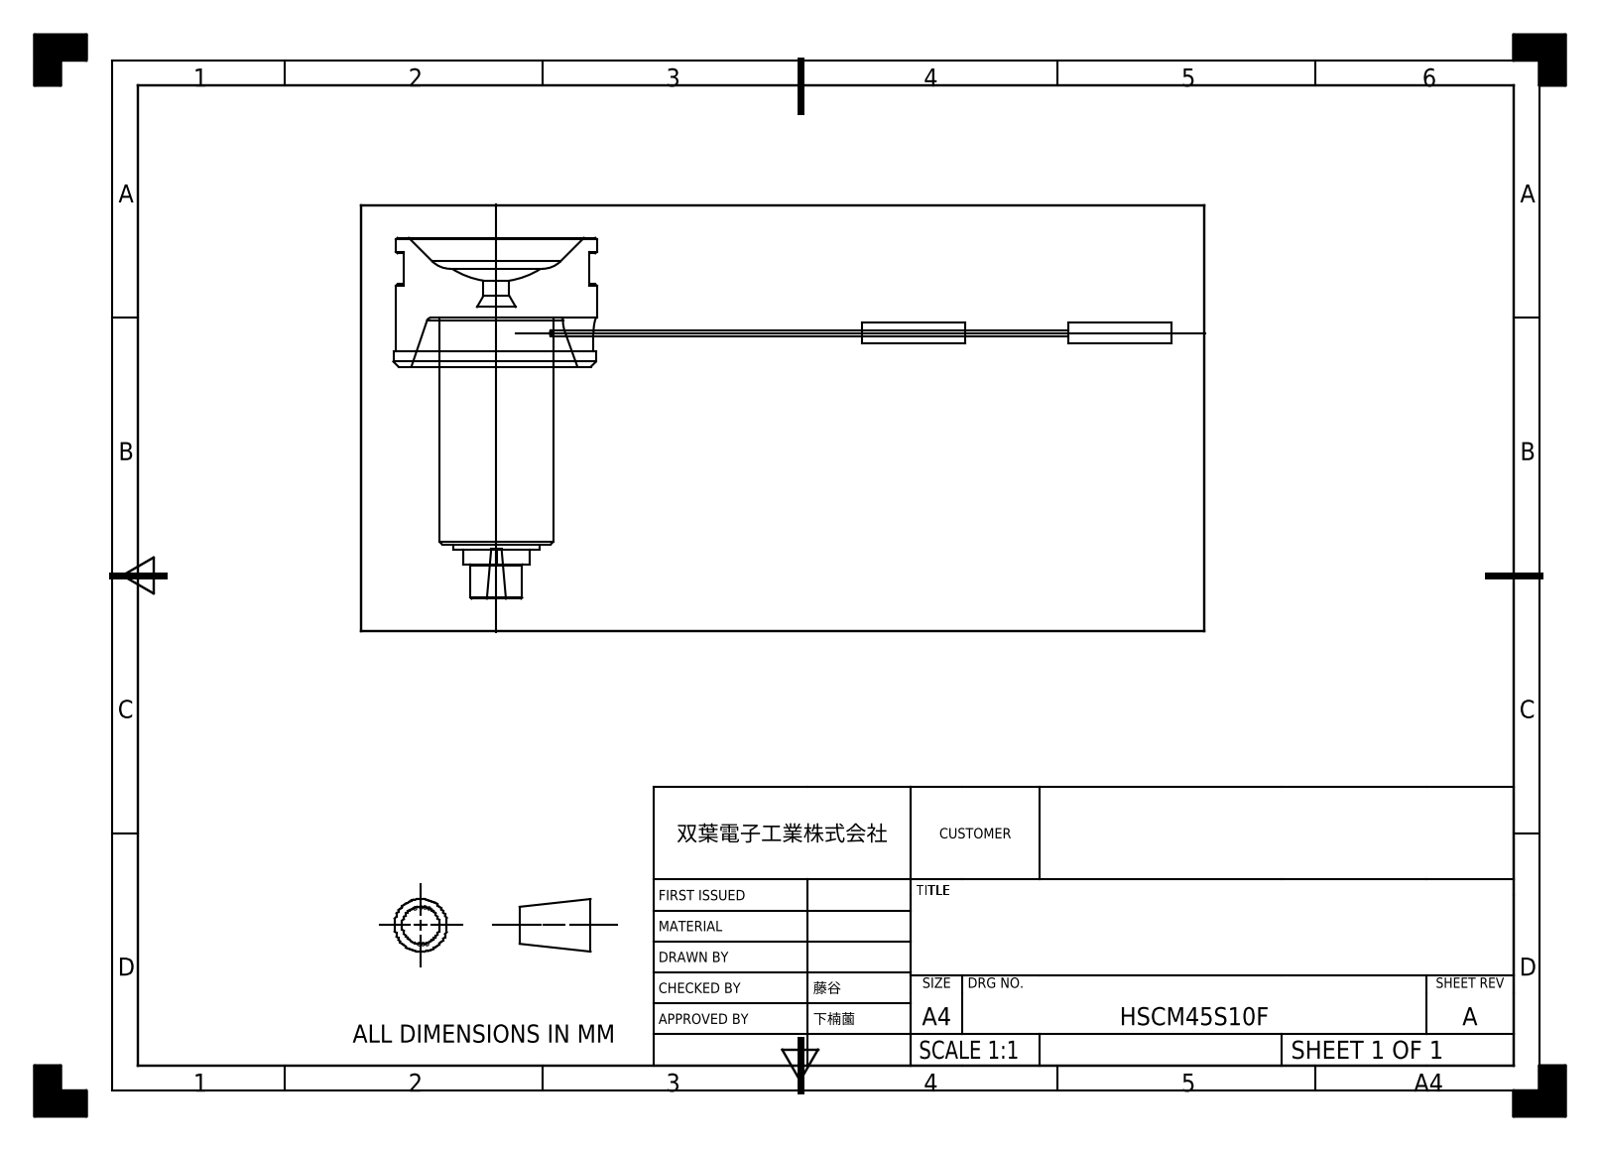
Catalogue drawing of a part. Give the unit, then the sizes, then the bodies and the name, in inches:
Units: inches
Overall size (bounding box): 5.945 × 2.756 × 1.575
Round holes (diameter × count): ⌀0.197 ×1
Round bosses / shafts (diameter × count): ⌀0.157 ×2, ⌀0.047 ×2, ⌀1.575 ×1, ⌀1.535 ×1, ⌀0.866 ×1, ⌀0.665 ×1, ⌀0.394 ×1
Partial cylindrical surfaces — rounded edges, fillets, slot ends (radius × count): R0.118 ×2, R0.293 ×1
Main face-to-face distances: 0.984, 0.374, 0.61, 1.772, 2.343, 1.732, 1.358, 0.118, 1.417, 0.512
Volume: 2.264 in³ · Surface area: 17.13 in²
Bodies: 1 solid, 63 faces (29 planar, 18 cylindrical, 16 other)
Part name (STEP PRODUCT): HSCM45S10F
STEP written by: SIEMENS PLM Software NX 2023 (AUTOMOTIVE_DESIGN)
